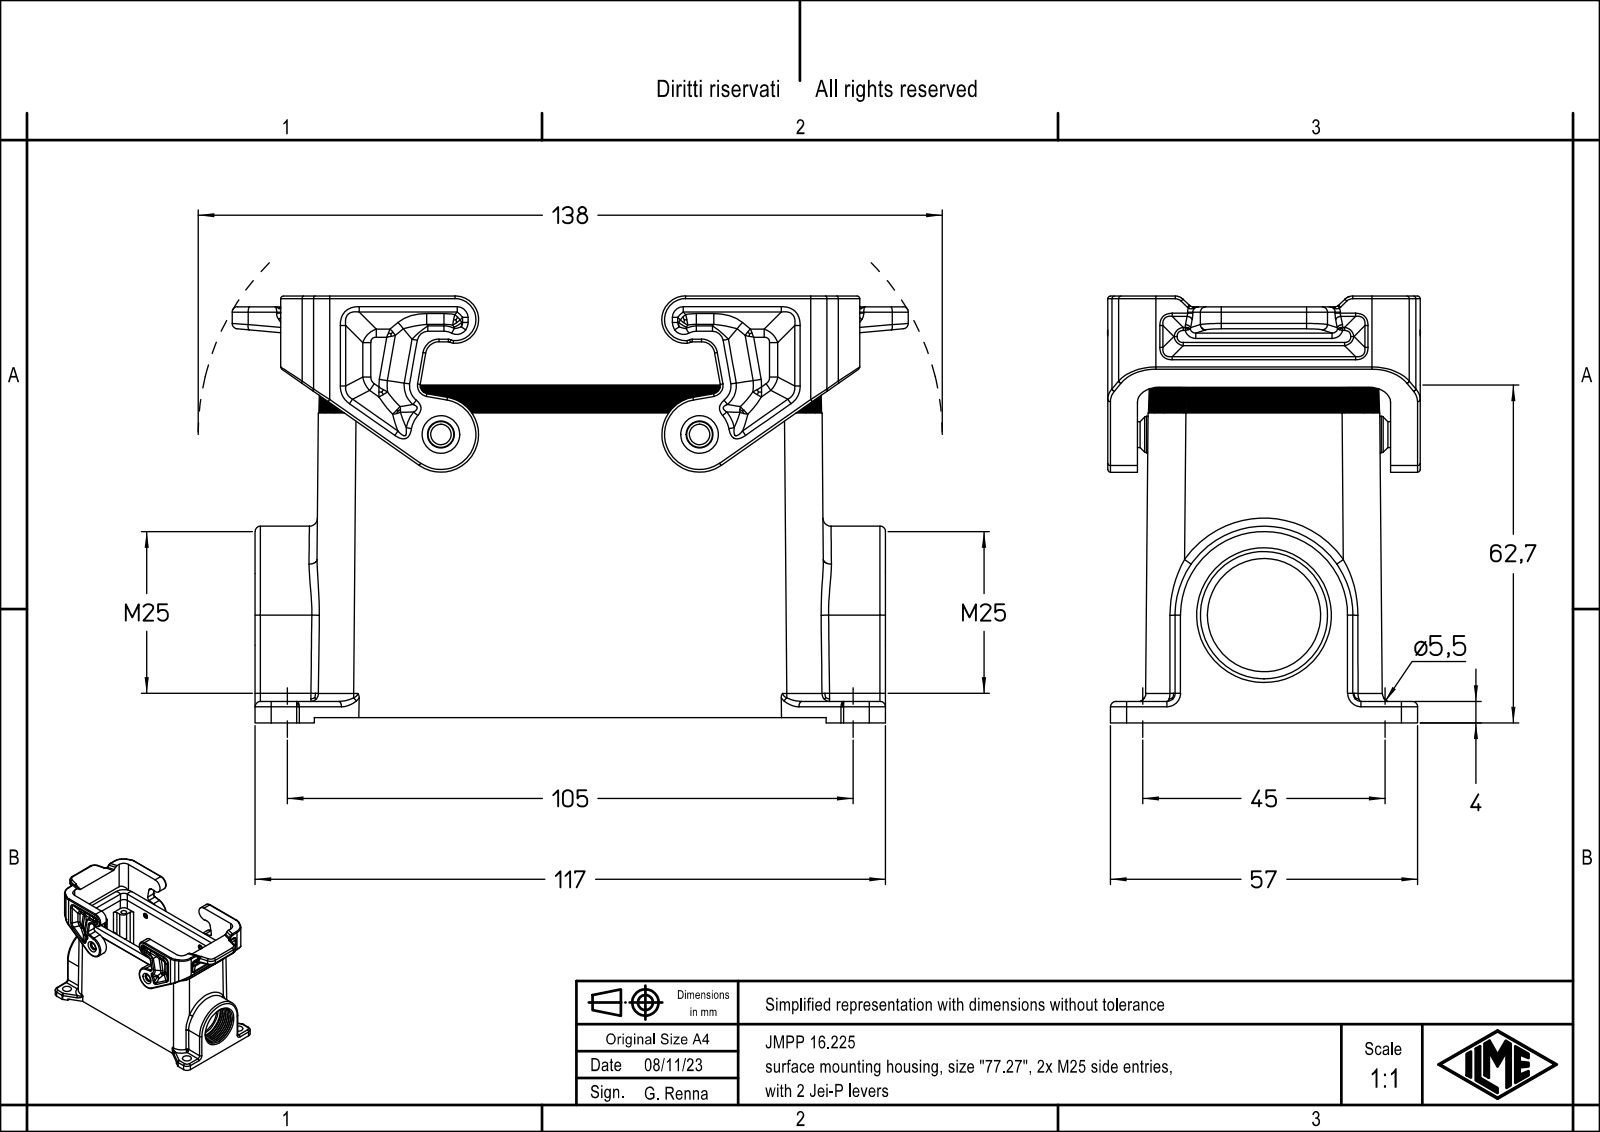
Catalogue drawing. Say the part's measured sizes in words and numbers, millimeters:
The part is named "JMPP 16.225". Its 3-D file was written by "Creo Elements/Direct Modeling 20.1B 02-Apr-2019 (C) Parametric Technology GmbH (AUTOMOTIVE_DESIGN)". It is 1 solid with 894 faces: 171 planar, 315 cylindrical and 408 other. Overall it measures 125.5 by 79.2 by 58.08 millimeters. Its volume is 125 718 cubic millimeters and its surface area 56 774 square millimeters. Round holes: 4 of diameter 3, 4 of diameter 3.5, 4 of diameter 5.5, 2 of diameter 4.8, 1 of diameter 21, 1 of diameter 23.6. Round bosses or shafts: 2 of diameter 6.8. Partial cylindrical surfaces (rounded edges, fillets, slot ends): 50 of radius 0.5, 48 of radius 1, 38 of radius 3, 24 of radius 2, 16 of radius 1.5, 12 of radius 4, 12 of radius 6, 10 of radius 7. The main face-to-face distances are 3, 47, 7, 1, 4, 9.75, 107.25, 5.5, 52.5, 2. The hole center spacings are 16.43, 38.54, 91.69, 98.09, 27, 45, 77.5, 82.07.
